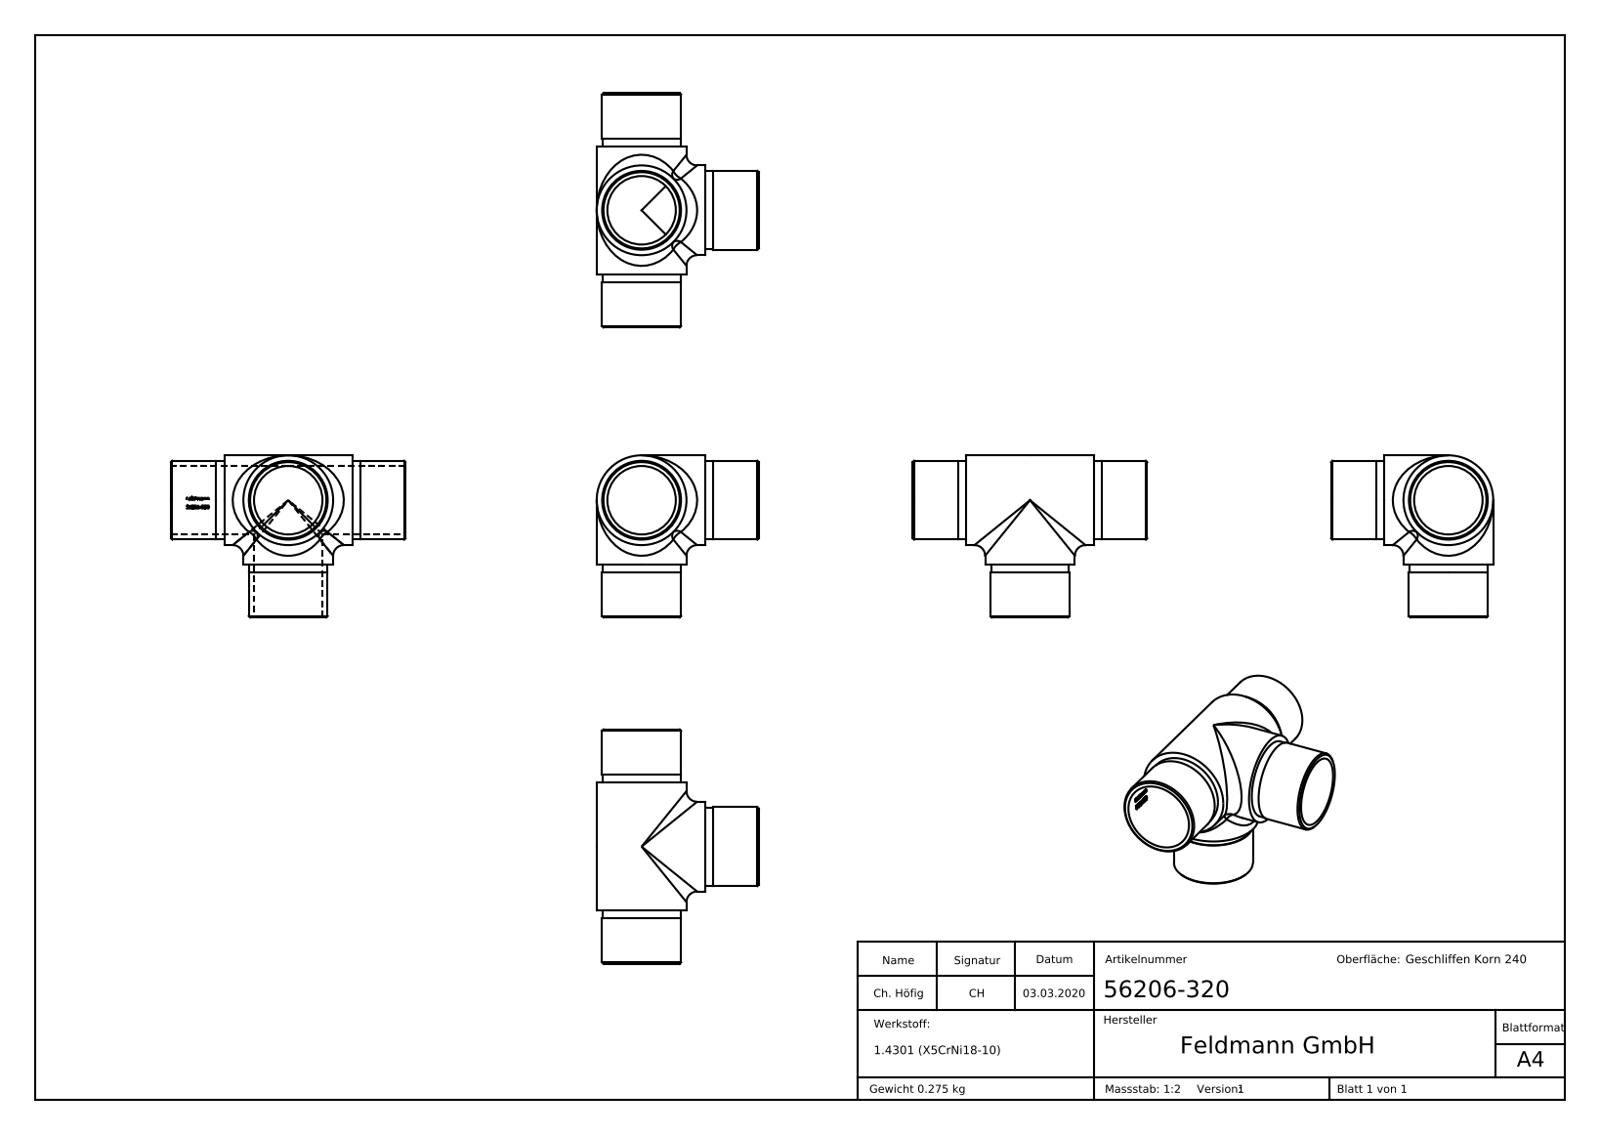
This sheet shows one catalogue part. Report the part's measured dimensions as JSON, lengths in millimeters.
{"part_name": "56206-320", "step_written_by": "SolidWorks 2015 (CONFIG_CONTROL_DESIGN)", "units": "millimeters", "bodies": {"solids": 1, "faces": 264, "planar": 97, "cylindrical": 38, "other": 129}, "overall_size": [88, 60.85, 60.85], "volume_mm3": 34822, "surface_area_mm2": 25787, "round_holes": [[25.7, 3]], "round_bosses_or_shafts": [[33.7, 3], [29.6, 3], [29.2, 3]], "partial_cylinders_radius": [[12.95, 1]], "face_to_face_distances": [20, 68, 48, 88, 3, 17, 71, 51, 54, 0.39]}
